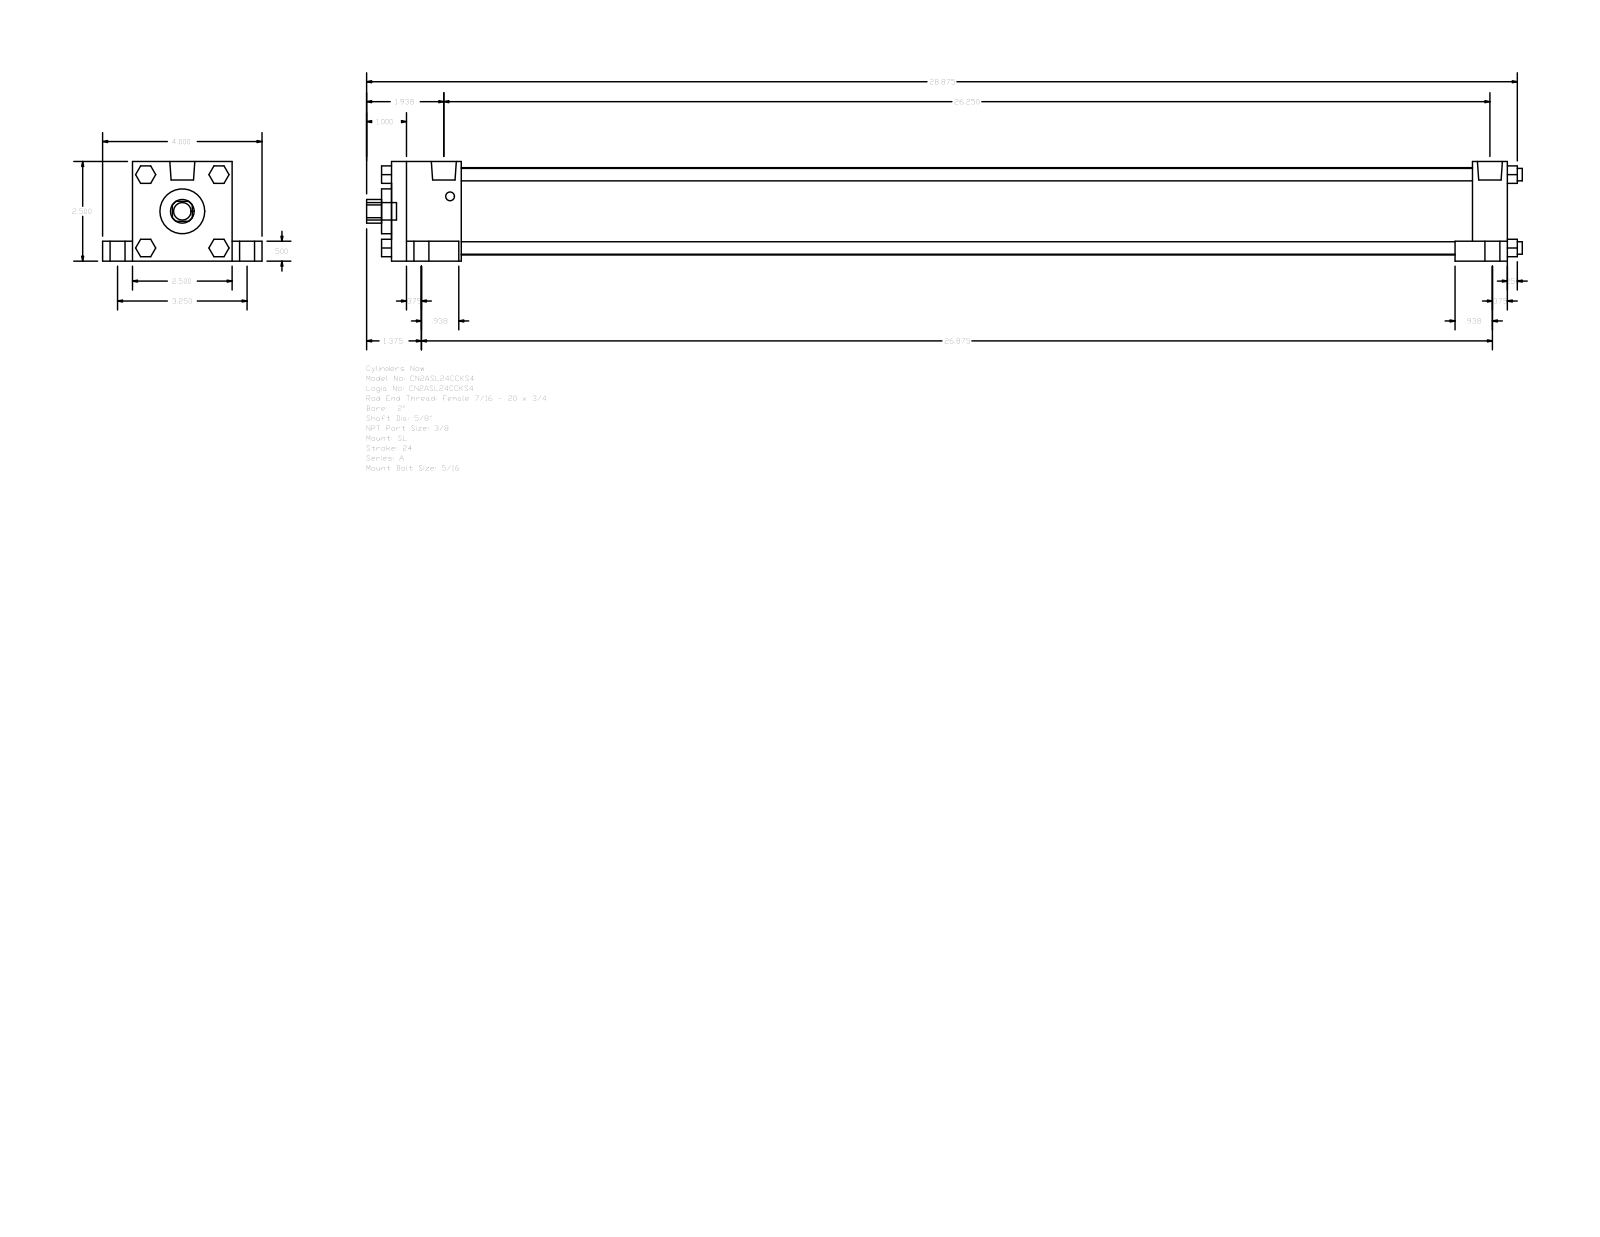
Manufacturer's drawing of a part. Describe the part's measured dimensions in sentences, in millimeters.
The part is named "A_SL__0200_0.625". Its 3-D file was written by "GSSL Pune (CONFIG_CONTROL_DESIGN)". It is 0 solids with 148 faces: 112 planar, 36 cylindrical and 0 other. Overall it measures 736.6 by 101.6 by 63.5 millimeters. Round holes: 1 of diameter 15.88, 1 of diameter 28.57, 1 of diameter 55.63. Round bosses or shafts: 4 of diameter 15.88, 4 of diameter 9.53, 4 of diameter 7.94, 4 of diameter 5.56, 2 of diameter 15.93, 1 of diameter 11.11. Partial cylindrical surfaces (rounded edges, fillets, slot ends): 1 of radius 7.54. The main face-to-face distances are 63.5, 711.2, 50.8, 12.7, 19.05, 82.55, 44.45, 666.75, 688.97, 644.52.
